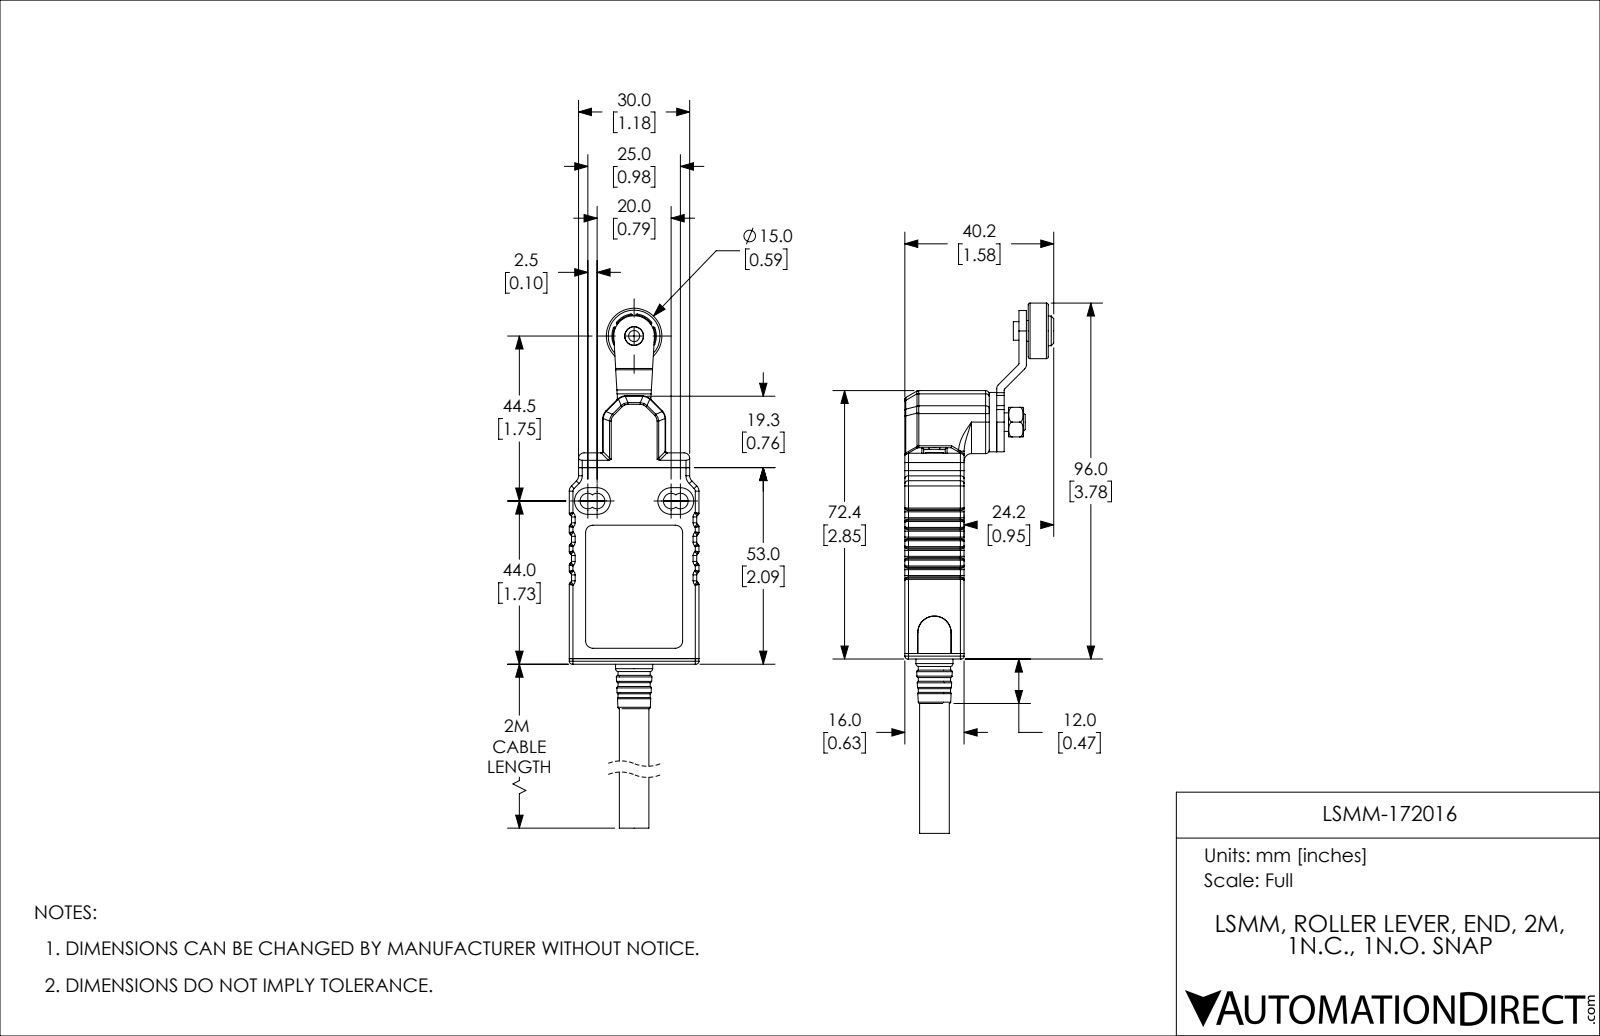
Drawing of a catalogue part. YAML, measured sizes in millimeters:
part_name: "170-LSPM-Roller Lever-Bottom Cable (STEP format)"
step_written_by: "SolidWorks 2013 (CONFIG_CONTROL_DESIGN)"
units: millimeters
bodies: {solids: 13, faces: 1110, planar: 328, cylindrical: 483, other: 299}
overall_size: [143, 40.2, 35]
volume: 23912
surface_area: 23761
round_holes:
  - {diameter: 2, count: 2}
  - {diameter: 2.5, count: 2}
  - {diameter: 3.1, count: 2}
  - {diameter: 3, count: 1}
  - {diameter: 4, count: 1}
  - {diameter: 5, count: 1}
  - {diameter: 5.1, count: 1}
  - {diameter: 5.7, count: 1}
  - {diameter: 8, count: 1}
  - {diameter: 9, count: 1}
  - {diameter: 10, count: 1}
  - {diameter: 11.1, count: 1}
round_bosses_or_shafts:
  - {diameter: 4.7, count: 2}
  - {diameter: 16, count: 1}
  - {diameter: 15, count: 1}
  - {diameter: 13.3, count: 1}
  - {diameter: 11, count: 1}
  - {diameter: 10.6, count: 1}
  - {diameter: 9.8, count: 1}
  - {diameter: 8.7, count: 1}
partial_cylinders:
  - {radius: 0.5, count: 91}
  - {radius: 1, count: 64}
  - {radius: 0.3, count: 39}
  - {radius: 1.5, count: 8}
  - {radius: 2, count: 8}
  - {radius: 3, count: 8}
  - {radius: 0.8, count: 4}
  - {radius: 2.1, count: 4}
face_to_face_distances: [1.5, 15.7, 14.5, 1.2, 14.2, 1, 2.5, 2, 13, 15.4]
hole_center_spacings: [12, 24, 24.6]
